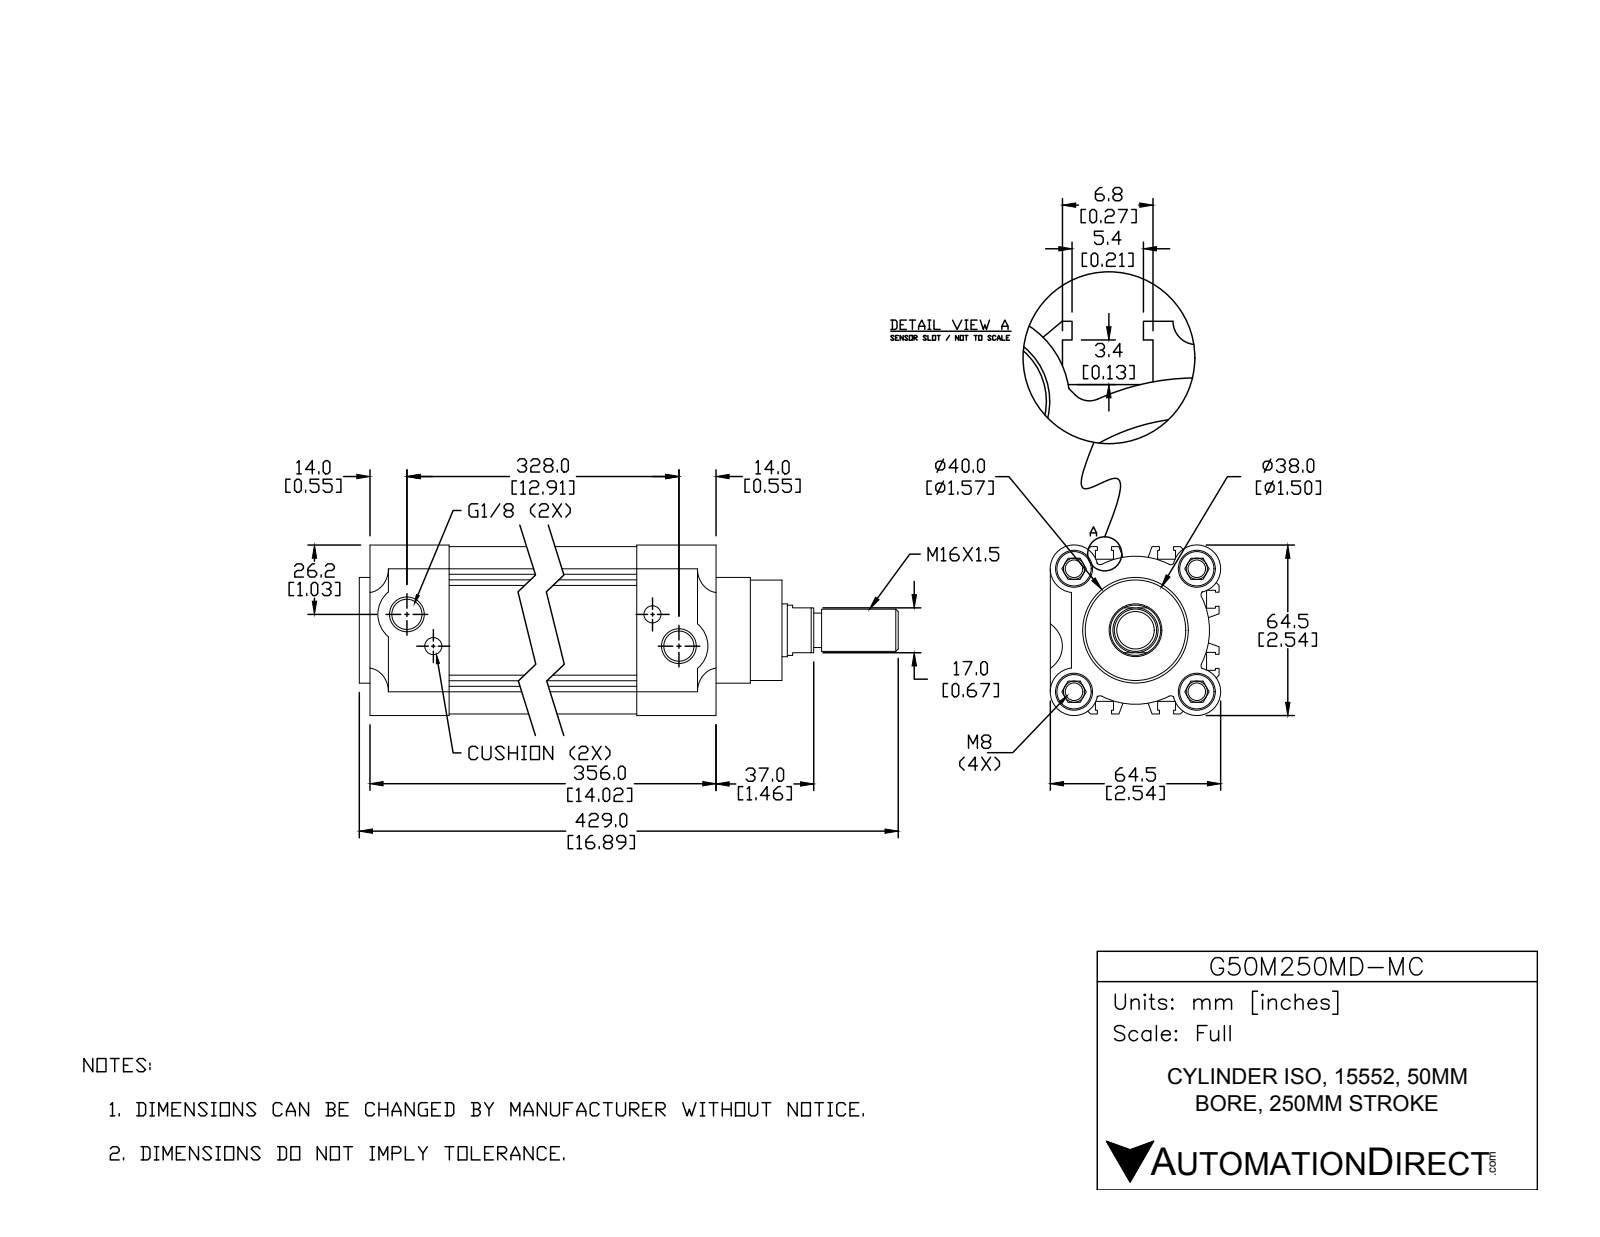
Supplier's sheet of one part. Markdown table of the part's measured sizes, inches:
| quantity | value |
| --- | --- |
| part name | 50121250-R; G50M250MD-MC; 50-250-90.5-B; 50-HL (+1 more) |
| STEP written by | SolidWorks 2015 (CONFIG_CONTROL_DESIGN) |
| units | inches |
| bodies | 4 solids, 418 faces (236 planar, 138 cylindrical, 44 other) |
| overall size | 16.89 × 2.539 × 2.539 |
| volume | 54.37 in³ |
| surface area | 375 in² |
| round holes (diameter × count) | 0.262 × 4, 0.551 × 4, 0.256 × 2, 0.262 × 2, 0.451 × 2, 0.787 × 1 |
| round bosses / shafts (diameter × count) | 0.512 × 5, 1.969 × 1, 1.575 × 1, 1.496 × 1, 0.748 × 1, 0.63 × 1 |
| partial cylindrical surfaces (radius × count) | 0.059 × 12, 0.004 × 6, 0.331 × 4, 0.354 × 4, 0.433 × 2, 1.083 × 1, 1.102 × 1 |
| main face-to-face distances | 0.187, 2.305, 2.492, 1.062, 1.645, 0.925, 1.575, 0.65, 0.917, 1.843 |
| hole center spacings | 1.294, 1.831, 0.615, 2.589, 12.52, 12.135, 12.922 |
